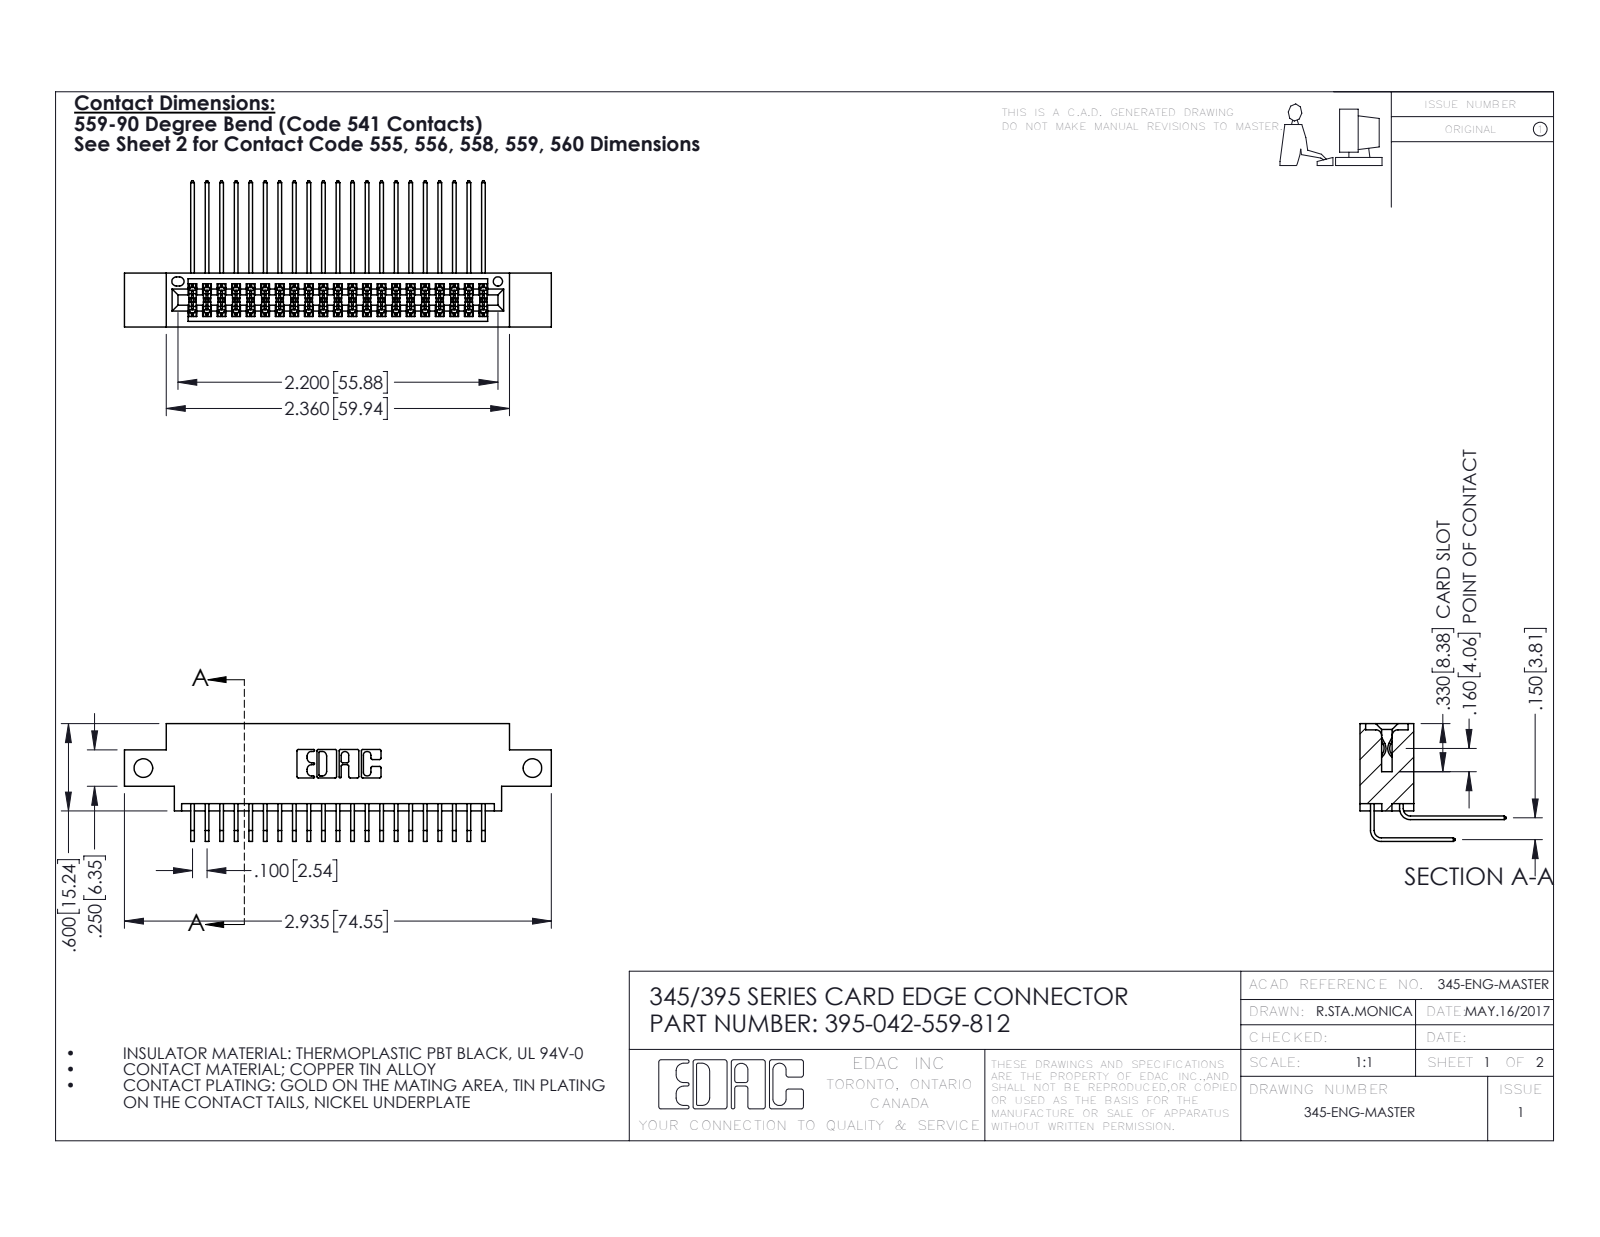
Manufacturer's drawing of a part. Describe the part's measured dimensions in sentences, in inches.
The part is named "345-292-001_558 559 Tail - 1; 395-042-559-812; 345-292-001_559 Tail - 2; 345 Part_0.170 Offset - Side Mount". Its 3-D file was written by "SolidWorks 2016 (CONFIG_CONTROL_DESIGN)". It is 43 solids with 2314 faces: 1554 planar, 760 cylindrical and 0 other. Overall it measures 2.935 by 1.005 by 0.809 inches. Its volume is 0.433 cubic inches and its surface area 17.39 square inches. Round holes: 2 of diameter 0.128, 1 of diameter 0.064. Partial cylindrical surfaces (rounded edges, fillets, slot ends): 64 of radius 0.006, 22 of radius 0.01, 6 of radius 0.007, 6 of radius 0.031, 3 of radius 0.026, 2 of radius 0.014, 2 of radius 0.019, 2 of radius 0.022. The main face-to-face distances are 0.072, 0.298, 0.37, 0.2, 0.098, 0.272, 0.025, 0.15, 0.225, 0.175. The hole center spacings are 2.675.
